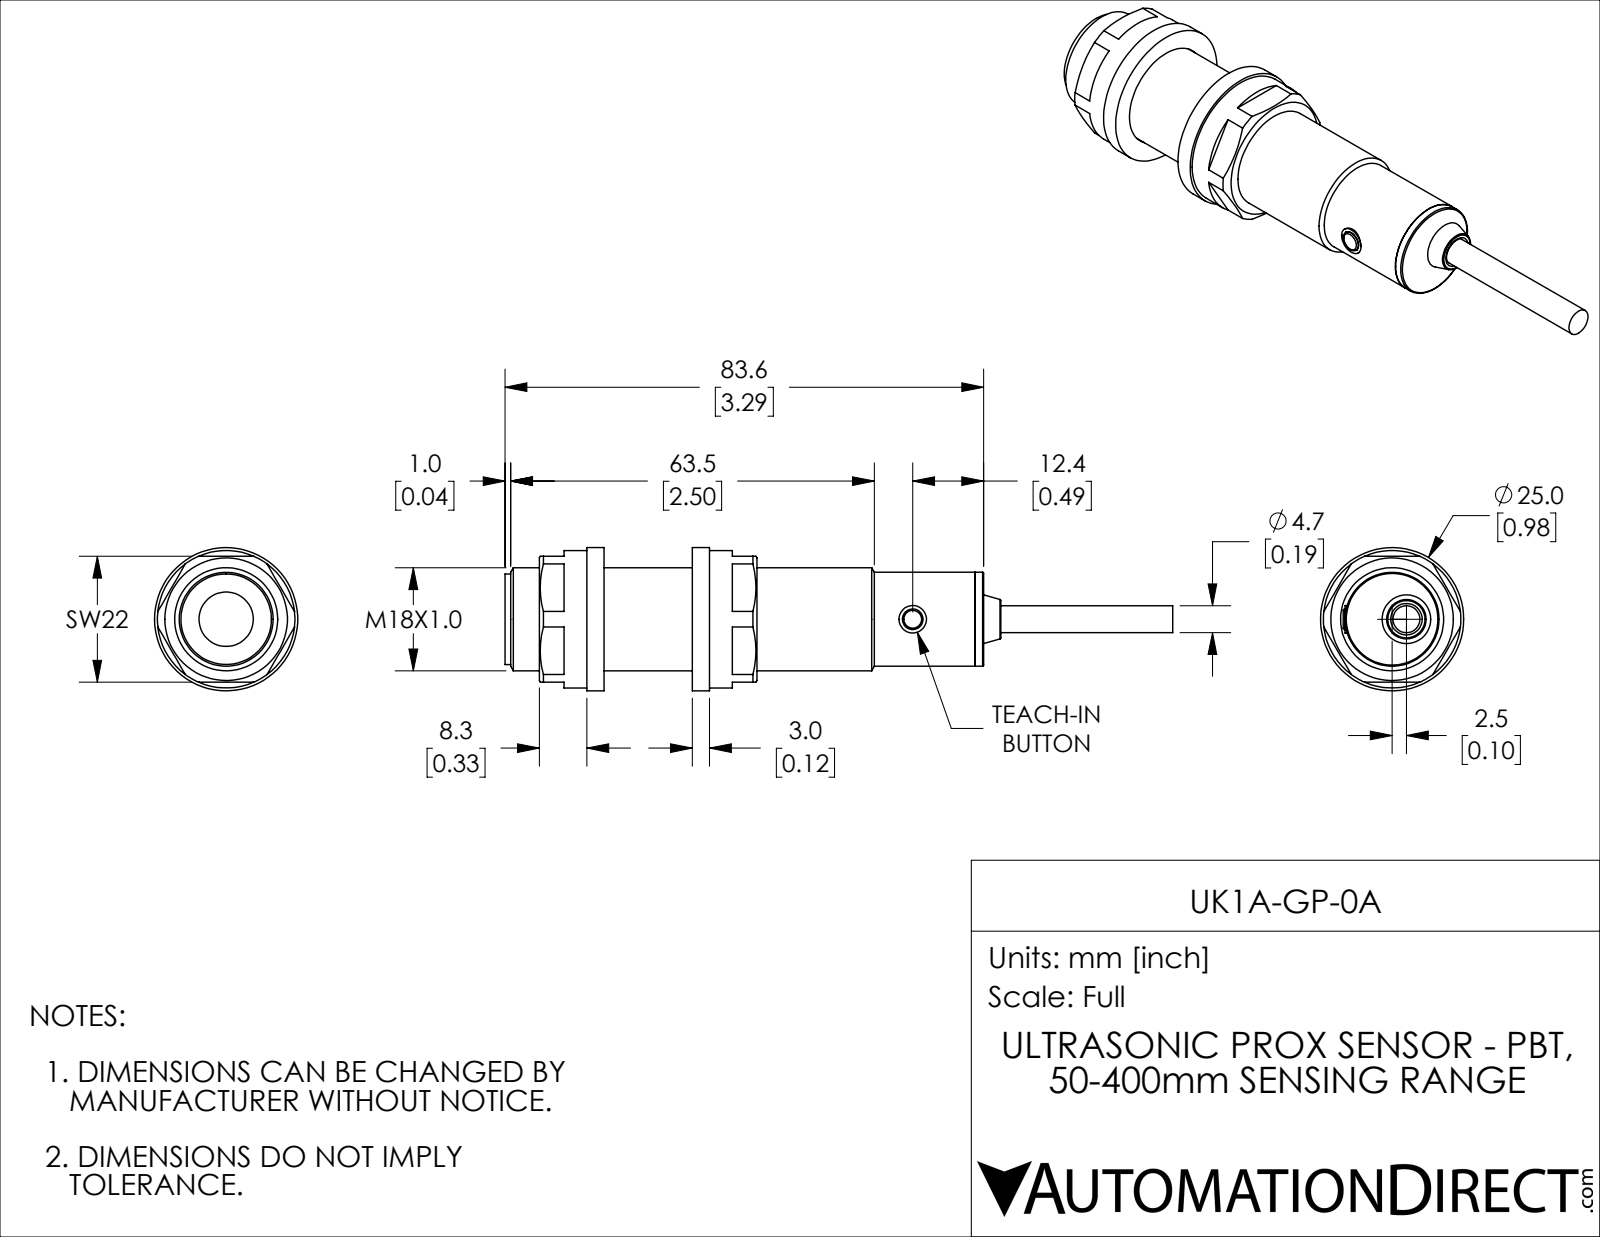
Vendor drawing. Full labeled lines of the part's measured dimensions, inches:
Part name (STEP PRODUCT): UK1A-GP-0A
STEP written by: SolidWorks 2018 (AUTOMOTIVE_DESIGN)
Units: inches
Bodies: 10 solids, 107 faces (49 planar, 40 cylindrical, 18 other)
Overall size (bounding box): 4.591 × 0.984 × 0.984
Volume: 1.539 in³ · Surface area: 17.7 in²
Round holes (diameter × count): ⌀0.185 ×2, ⌀0.142 ×1, ⌀0.374 ×1, ⌀0.709 ×1, ⌀0.717 ×1
Round bosses / shafts (diameter × count): ⌀0.984 ×1, ⌀0.945 ×1, ⌀0.646 ×1, ⌀0.622 ×1, ⌀0.213 ×1, ⌀0.189 ×1
Main face-to-face distances: 0.118, 0.724, 0.843, 2.669, 1.827, 0.524, 1.366, 3.193, 0.642, 2.551
Hole centre spacings: 0.098
